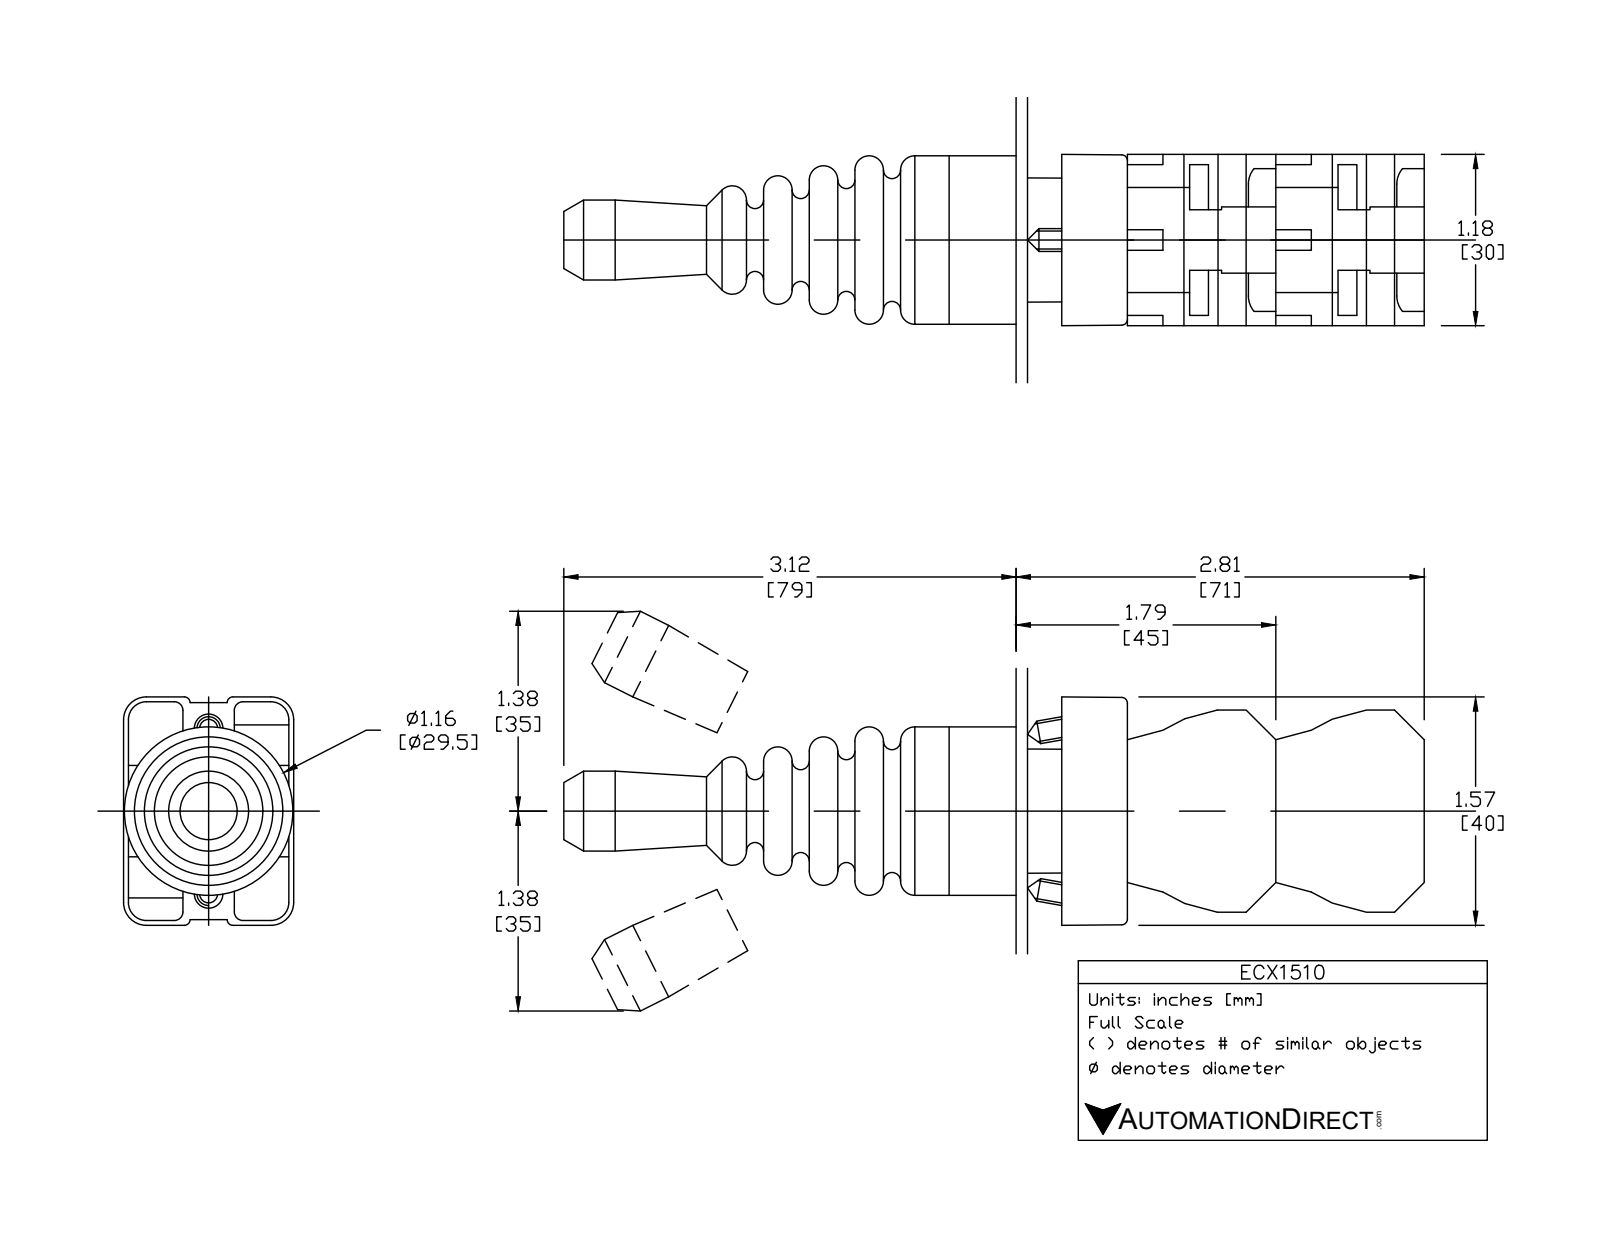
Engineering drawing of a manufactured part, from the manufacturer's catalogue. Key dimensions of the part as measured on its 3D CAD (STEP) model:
Part name (STEP PRODUCT): ECX1510
STEP written by: SolidWorks 2017 (AUTOMOTIVE_DESIGN)
Units: inches
Bodies: 7 solids, 521 faces (300 planar, 144 cylindrical, 77 other)
Overall size (bounding box): 4.886 × 1.581 × 1.181
Volume: 3.568 in³ · Surface area: 37.85 in²
Round holes (diameter × count): ⌀0.079 ×4, ⌀0.087 ×2, ⌀0.124 ×2, ⌀0.13 ×2, ⌀0.197 ×1, ⌀0.878 ×1, ⌀0.888 ×1
Round bosses / shafts (diameter × count): ⌀0.157 ×2, ⌀1.181 ×1, ⌀1.175 ×1, ⌀0.945 ×1, ⌀0.856 ×1, ⌀0.78 ×1
Partial cylindrical surfaces — rounded edges, fillets, slot ends (radius × count): R0.059 ×24, R0.041 ×12, R0.124 ×12, R0.157 ×12, R0.039 ×4, R0.063 ×2, R0.079 ×2, R0.128 ×2
Main face-to-face distances: 0.591, 0.579, 1.193, 1.169, 0.033, 0.031, 1.024, 2.217, 1.055, 1.161
Hole centre spacings: 0.236, 0.636, 0.591, 0.257, 0.472, 0.544, 0.756, 0.1
